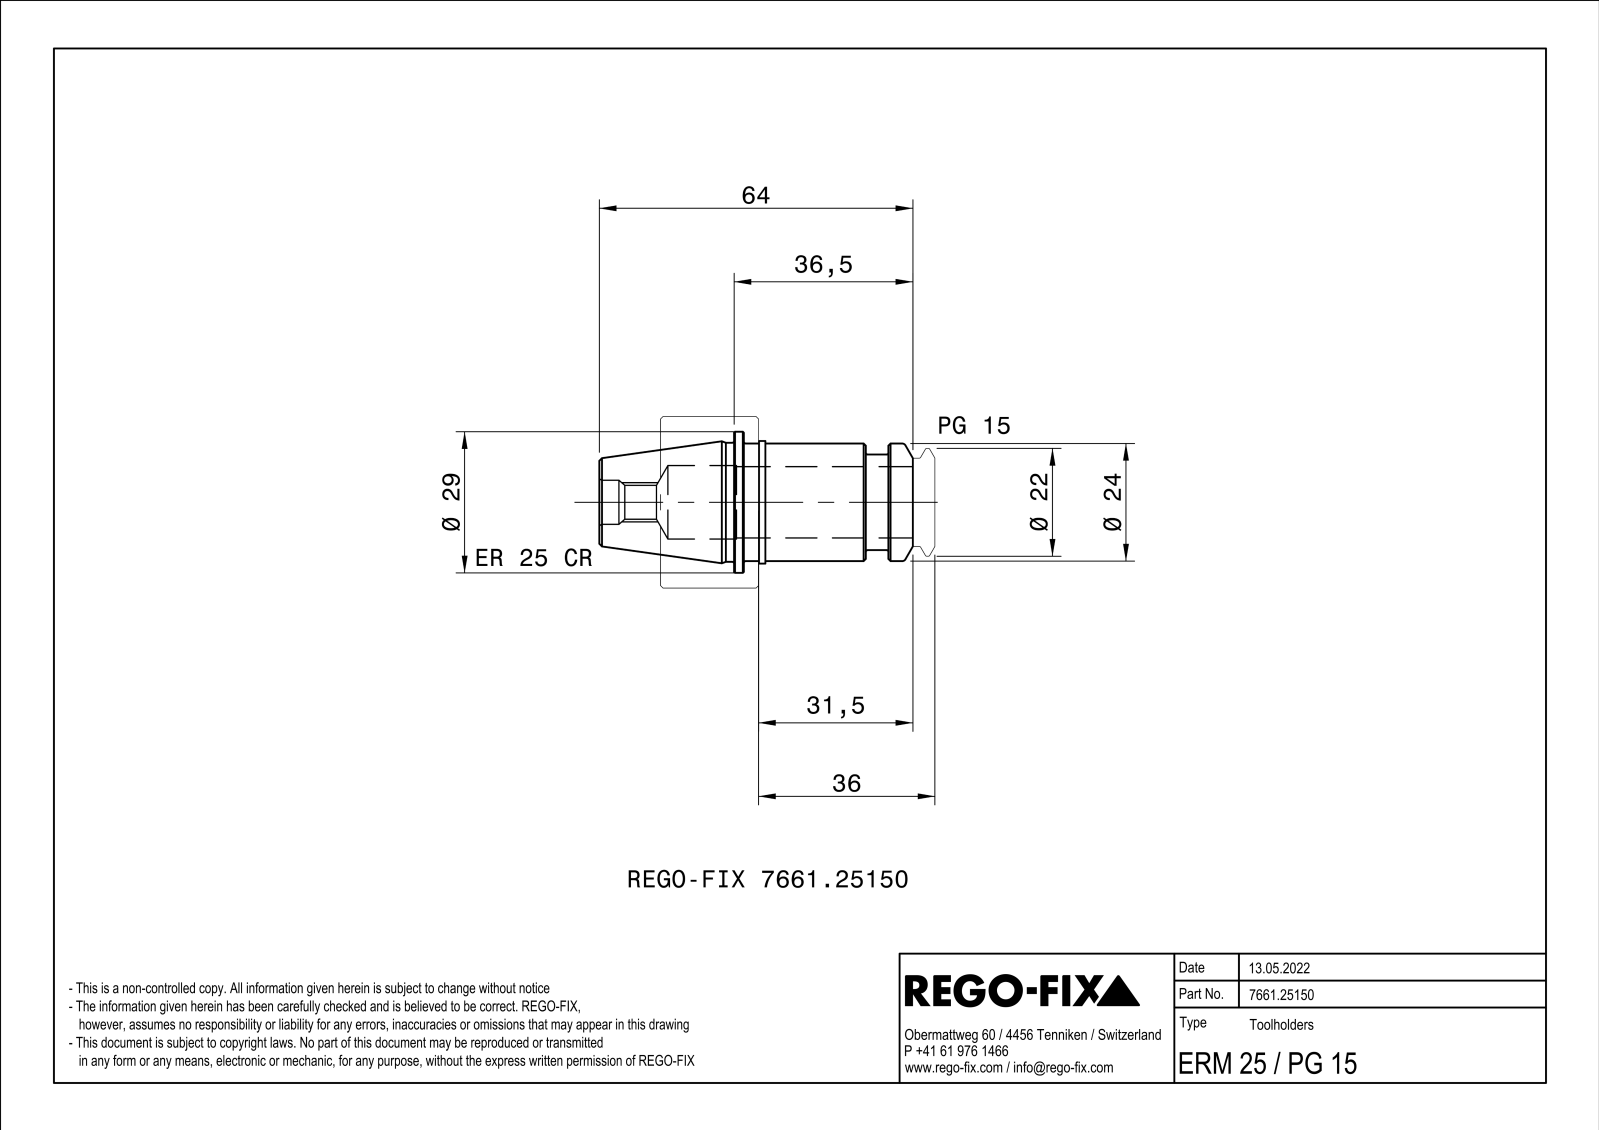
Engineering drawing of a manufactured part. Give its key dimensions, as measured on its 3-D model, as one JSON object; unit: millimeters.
{"part_name": "NOCUT", "step_written_by": "SIEMENS PLM Software Solid Edge ST10 (AUTOMOTIVE_DESIGN)", "units": "millimeters", "bodies": {"solids": 1, "faces": 78, "planar": 34, "cylindrical": 15, "other": 29}, "overall_size": [64, 35, 35], "volume_mm3": 20862, "surface_area_mm2": 12102, "round_holes": [[6.92, 1], [9, 1], [15, 1], [24.4, 1], [29, 1], [30.4, 1]], "round_bosses_or_shafts": [[35, 1], [28.9, 1], [28.8, 1], [24.3, 1], [24, 1], [22.4, 1], [19.5, 1]], "face_to_face_distances": [5, 1.2, 1.4, 14.4, 13.2, 13, 29.5, 33.9, 32.7, 32.5]}
